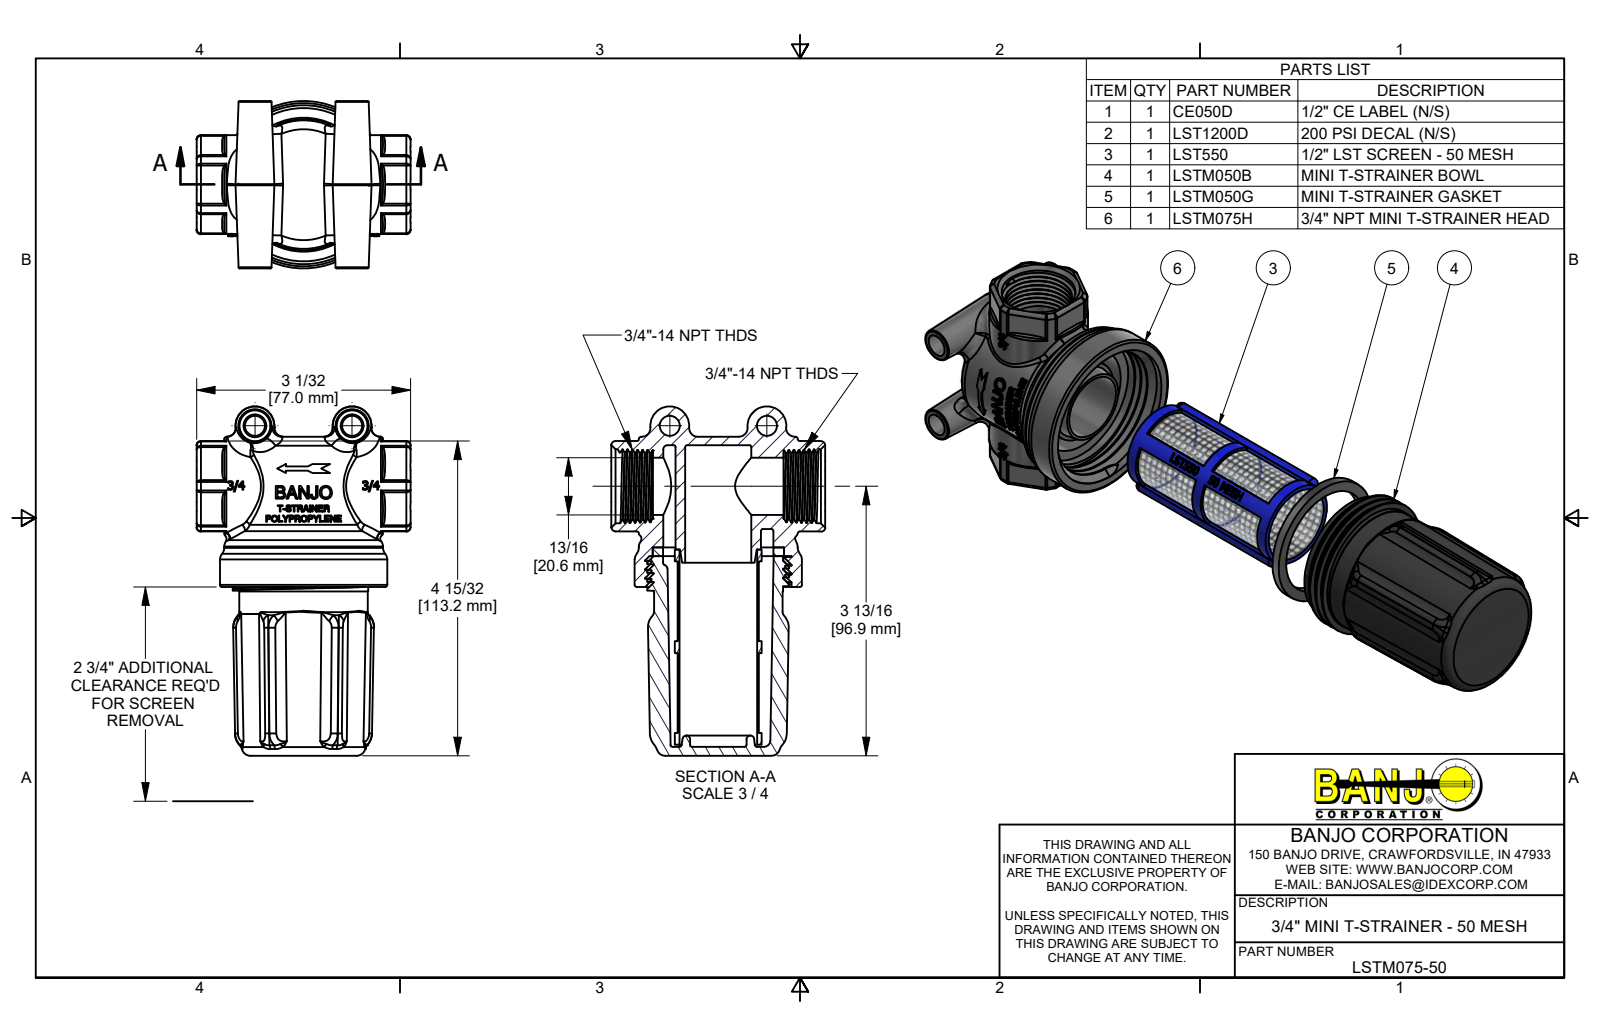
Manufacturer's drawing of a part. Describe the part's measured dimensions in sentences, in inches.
The part is named "LSTM075-50; LSTM075H; LSTM050G; LST550 (+1 more)". Its 3-D file was written by "Autodesk Inventor 2019 (AUTOMOTIVE_DESIGN)". It is 4 solids with 1403 faces: 580 planar, 184 cylindrical and 639 other. Overall it measures 4.947 by 3.03 by 2.37 inches. Its volume is 7.756 cubic inches and its surface area 124.7 square inches. Round holes: 1 of diameter 0.8, 1 of diameter 0.81, 1 of diameter 0.937, 1 of diameter 1.101, 1 of diameter 1.56, 1 of diameter 1.563, 1 of diameter 1.891, 1 of diameter 2.073. Round bosses or shafts: 1 of diameter 2.37, 1 of diameter 2.25, 1 of diameter 2.01, 1 of diameter 1.861, 1 of diameter 1.86, 1 of diameter 1.833, 1 of diameter 1.82, 1 of diameter 1.4. Partial cylindrical surfaces (rounded edges, fillets, slot ends): 24 of radius 0.06, 8 of radius 0.08, 4 of radius 0.03, 3 of radius 0.05, 2 of radius 0.084, 1 of radius 0.313, 1 of radius 0.55, 1 of radius 0.576. The main face-to-face distances are 2.825, 2.95, 0.125, 4.515, 1.69, 1.565, 1.28, 4.397, 1.572, 1.447.
